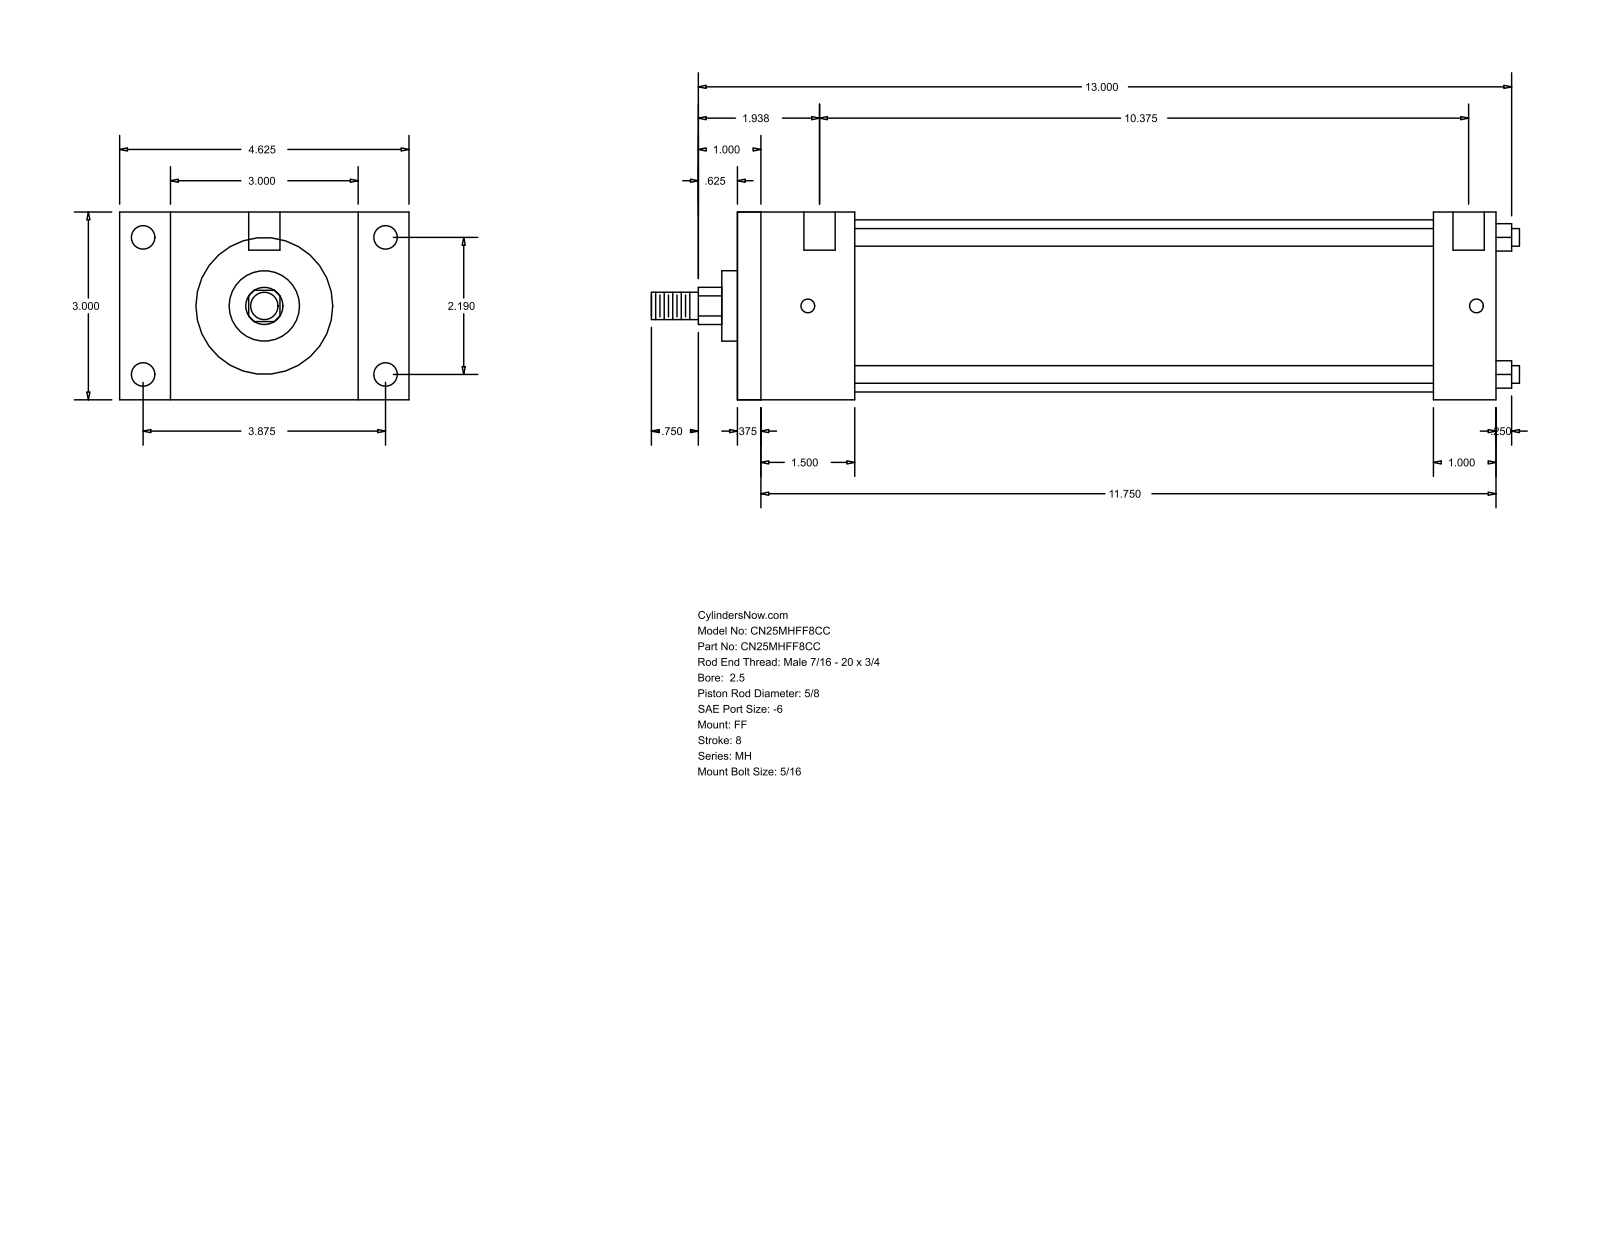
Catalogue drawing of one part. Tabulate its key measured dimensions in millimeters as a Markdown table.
| quantity | value |
| --- | --- |
| part name | MH_FF__0250_0.625 |
| STEP written by | GSSL Pune (CONFIG_CONTROL_DESIGN) |
| units | millimeters |
| bodies | 0 solids, 92 faces (64 planar, 28 cylindrical, 0 other) |
| overall size | 352.43 × 117.47 × 76.2 |
| round holes (diameter × count) | 5.56 × 4, 9.53 × 4, 12.7 × 2 |
| round bosses / shafts (diameter × count) | 7.14 × 4, 69.85 × 1, 28.57 × 1, 15.88 × 1, 11.11 × 1 |
| partial cylindrical surfaces (radius × count) | 7.54 × 1 |
| main face-to-face distances | 76.2, 307.97, 298.45, 9.52, 25.4, 47.62, 282.57, 38.1, 273.05, 234.95 |
| hole center spacings | 55.62, 98.42, 113.05, 271.46, 3.17, 4.76, 263.53, 266.7 |
